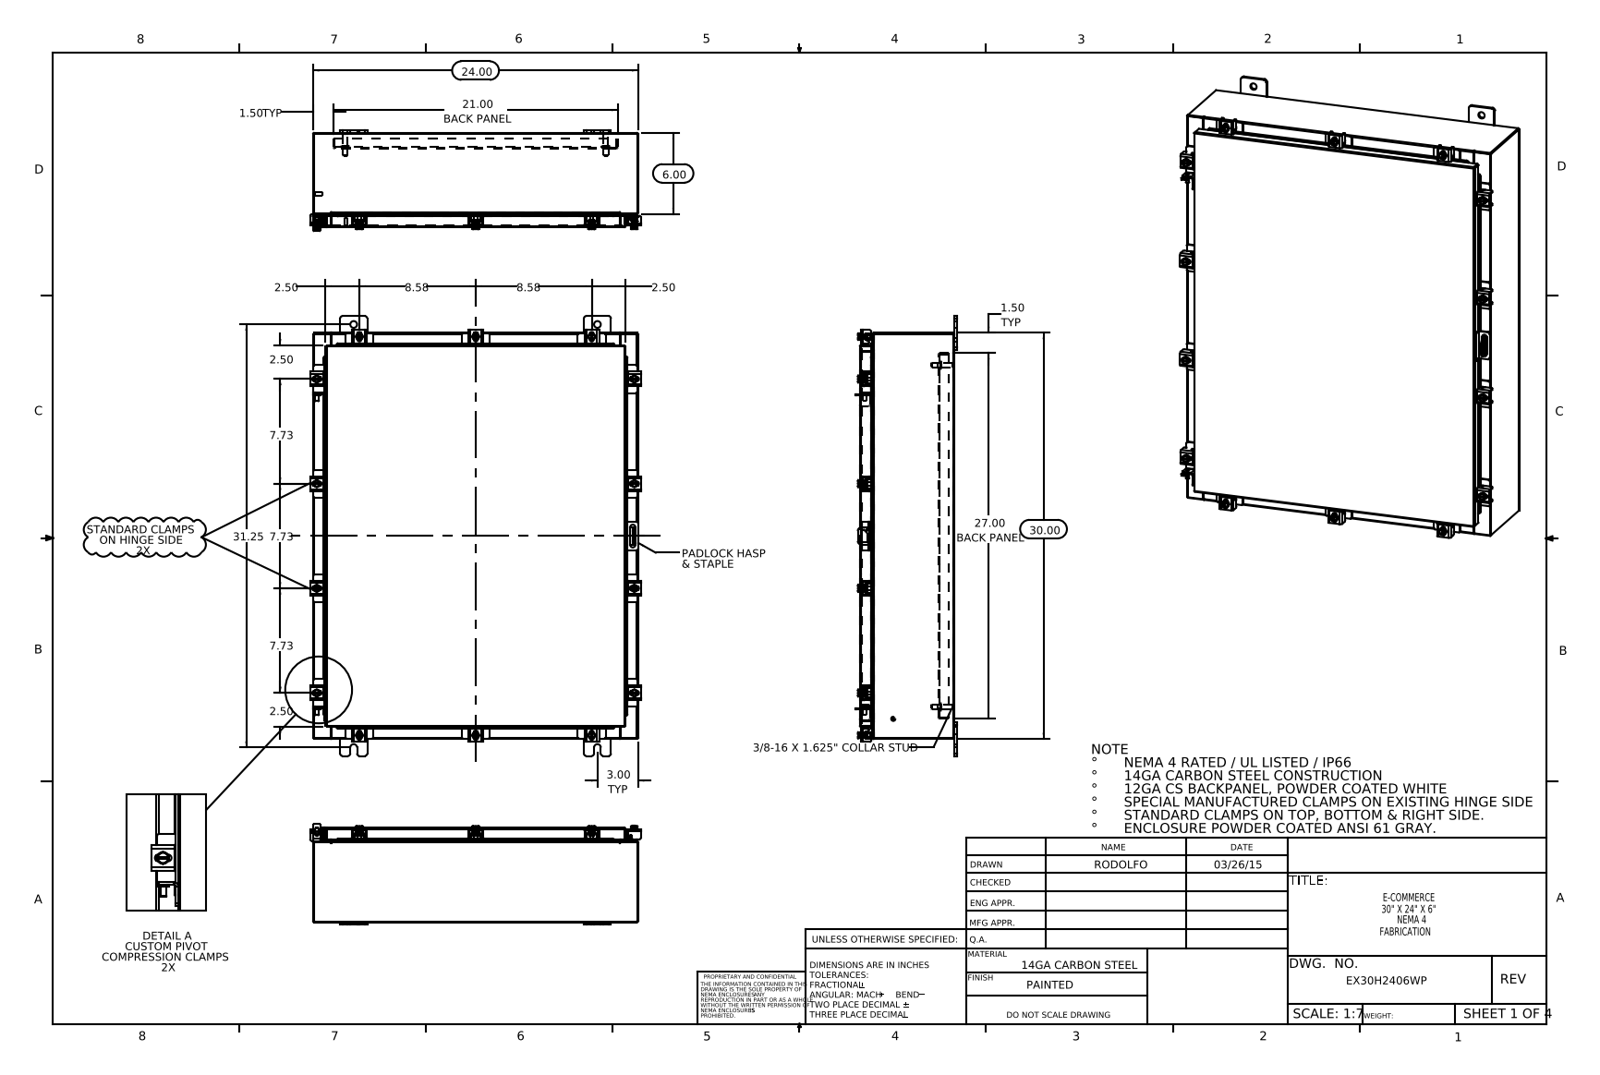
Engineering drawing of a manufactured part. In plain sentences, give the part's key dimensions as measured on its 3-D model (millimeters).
The part is named "HW-CLN-NH-20330; EX30H2406WP Backpanel; EX30H2406WP Cover; EX30H2406WP Padlock Hasp (+8 more)". Its 3-D file was written by "SolidWorks 2014 (CONFIG_CONTROL_DESIGN)". It is 91 solids with 2272 faces: 1211 planar, 885 cylindrical and 176 other. Overall it measures 825.5 by 620.3 by 189.3 millimeters. Its volume is 4 074 000 cubic millimeters and its surface area 3 963 000 square millimeters. Round holes: 14 of diameter 5.4, 14 of diameter 6.6, 8 of diameter 12.7, 1 of diameter 3.2, 1 of diameter 6.4. Round bosses or shafts: 14 of diameter 12.7, 14 of diameter 6.4, 12 of diameter 10.1, 4 of diameter 15.9, 4 of diameter 9.5, 4 of diameter 8.4, 2 of diameter 8, 2 of diameter 6. Partial cylindrical surfaces (rounded edges, fillets, slot ends): 62 of radius 1.5, 28 of radius 3.6, 26 of radius 0.3, 26 of radius 3, 24 of radius 4.8, 22 of radius 2.2, 20 of radius 2.3, 19 of radius 1.3. The main face-to-face distances are 1.9, 175.3, 177.2, 173.4, 2.6, 25.4, 27.3, 148, 149.9, 29.9. The hole center spacings are 59.6, 112.8, 521.8, 595.7, 617.5, 673.3, 695.2, 820.1.
